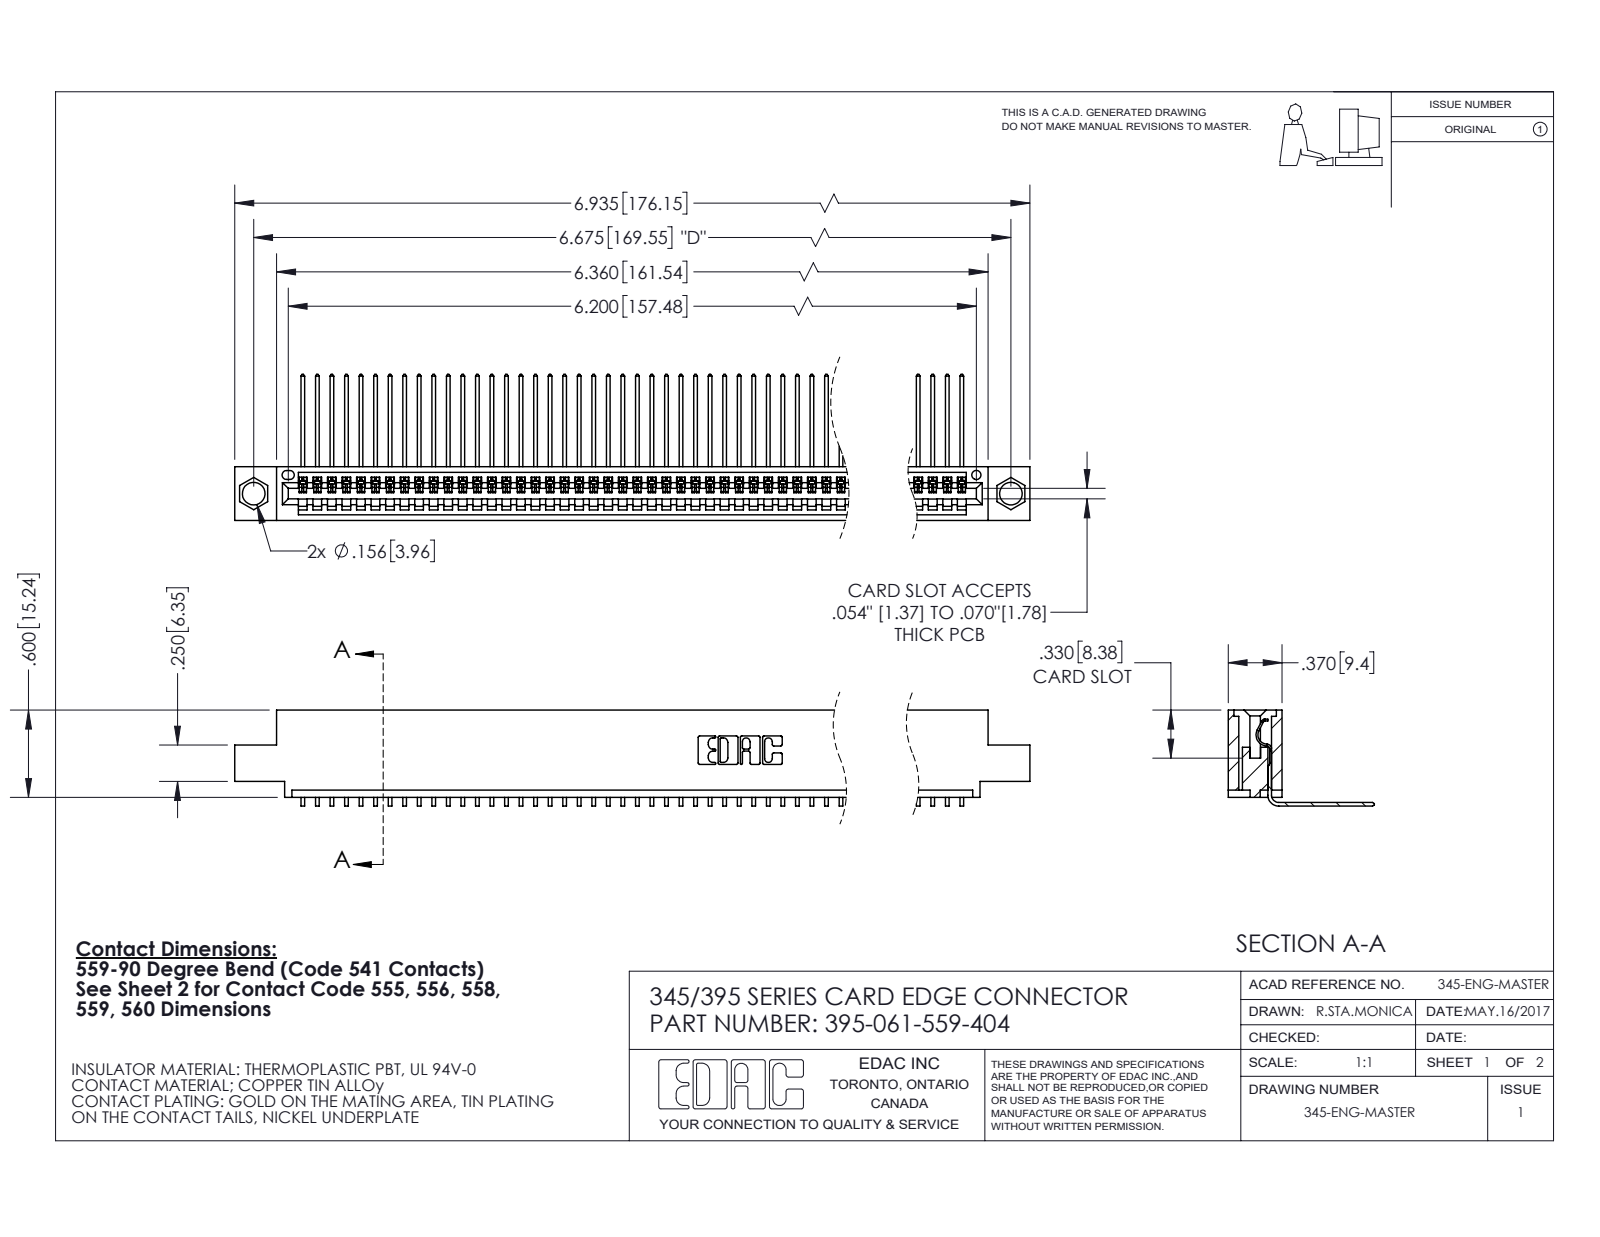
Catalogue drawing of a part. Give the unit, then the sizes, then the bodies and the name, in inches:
Units: inches
Overall size (bounding box): 6.935 × 1.005 × 0.659
Round holes (diameter × count): ⌀0.156 ×2, ⌀0.064 ×1
Partial cylindrical surfaces — rounded edges, fillets, slot ends (radius × count): R0.006 ×122, R0.01 ×22, R0.007 ×6, R0.031 ×6, R0.026 ×3, R0.031 ×2, R0.04 ×2, R0.014 ×1
Main face-to-face distances: 0.072, 0.298, 0.37, 0.2, 0.098, 0.272, 0.025, 0.225, 0.149, 0.072
Hole centre spacings: 0.27, 6.439, 6.675
Volume: 1.032 in³ · Surface area: 36.97 in²
Bodies: 62 solids, 3804 faces (2660 planar, 1144 cylindrical, 0 other)
Part name (STEP PRODUCT): 395-061-559-404; 345-292-001_558 559 Tail - 1; 345 Part_0.110 Offset - 0.156 Dia-TI
STEP written by: SolidWorks 2020 (CONFIG_CONTROL_DESIGN)
